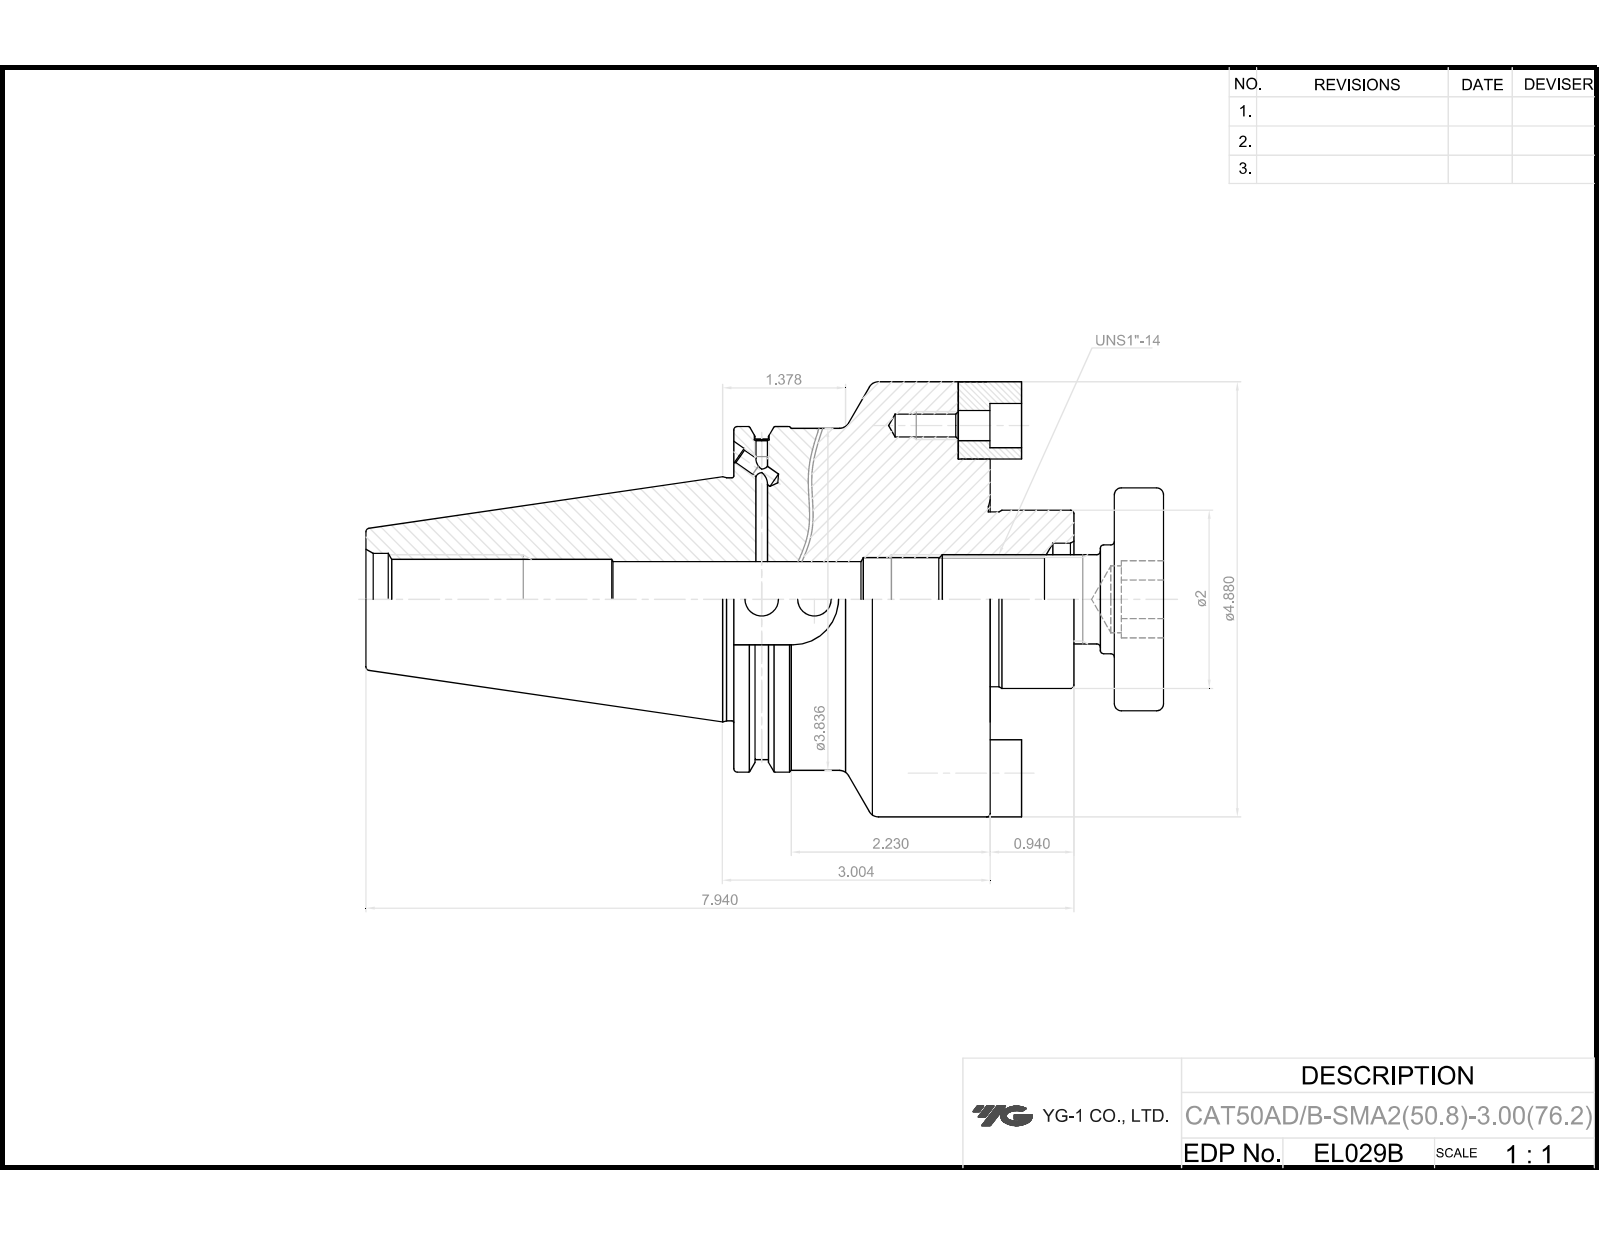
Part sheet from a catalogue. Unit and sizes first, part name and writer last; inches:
Units: inches
Overall size (bounding box): 9.081 × 4.882 × 4.88
Round holes (diameter × count): ⌀0.128 ×2, ⌀0.163 ×2, ⌀0.165 ×2, ⌀0.197 ×2, ⌀0.252 ×2, ⌀0.339 ×2, ⌀0.496 ×2, ⌀0.375 ×1, ⌀0.75 ×1, ⌀0.865 ×1, ⌀0.923 ×1, ⌀1.031 ×1
Round bosses / shafts (diameter × count): ⌀4.88 ×1, ⌀3.875 ×1, ⌀3.836 ×1, ⌀3.594 ×1, ⌀2.726 ×1, ⌀2.5 ×1, ⌀2 ×1, ⌀1.22 ×1
Partial cylindrical surfaces — rounded edges, fillets, slot ends (radius × count): R0.375 ×4, R0.51 ×1
Main face-to-face distances: 2.875, 4.957, 2.081, 4.406, 1.53, 0.551, 1.142, 2.518, 0.357, 1.887
Hole centre spacings: 1.949, 3.898
Volume: 60.44 in³ · Surface area: 163.4 in²
Bodies: 5 solids, 151 faces (75 planar, 45 cylindrical, 31 other)
Part name (STEP PRODUCT): LO-CAT50ADB-SMA50.8-76.2; HEX'' WRENCH BOLT-UNC5_16-18x3_4L; DRIVE KEY-19.05.x18x22; COLLAR BOLT-UNS1-14x50L
STEP written by: Autodesk Inventor 2025 (AP242_MANAGED_MODEL_BASED_3D_ENGINEERING_MIM_LF)
